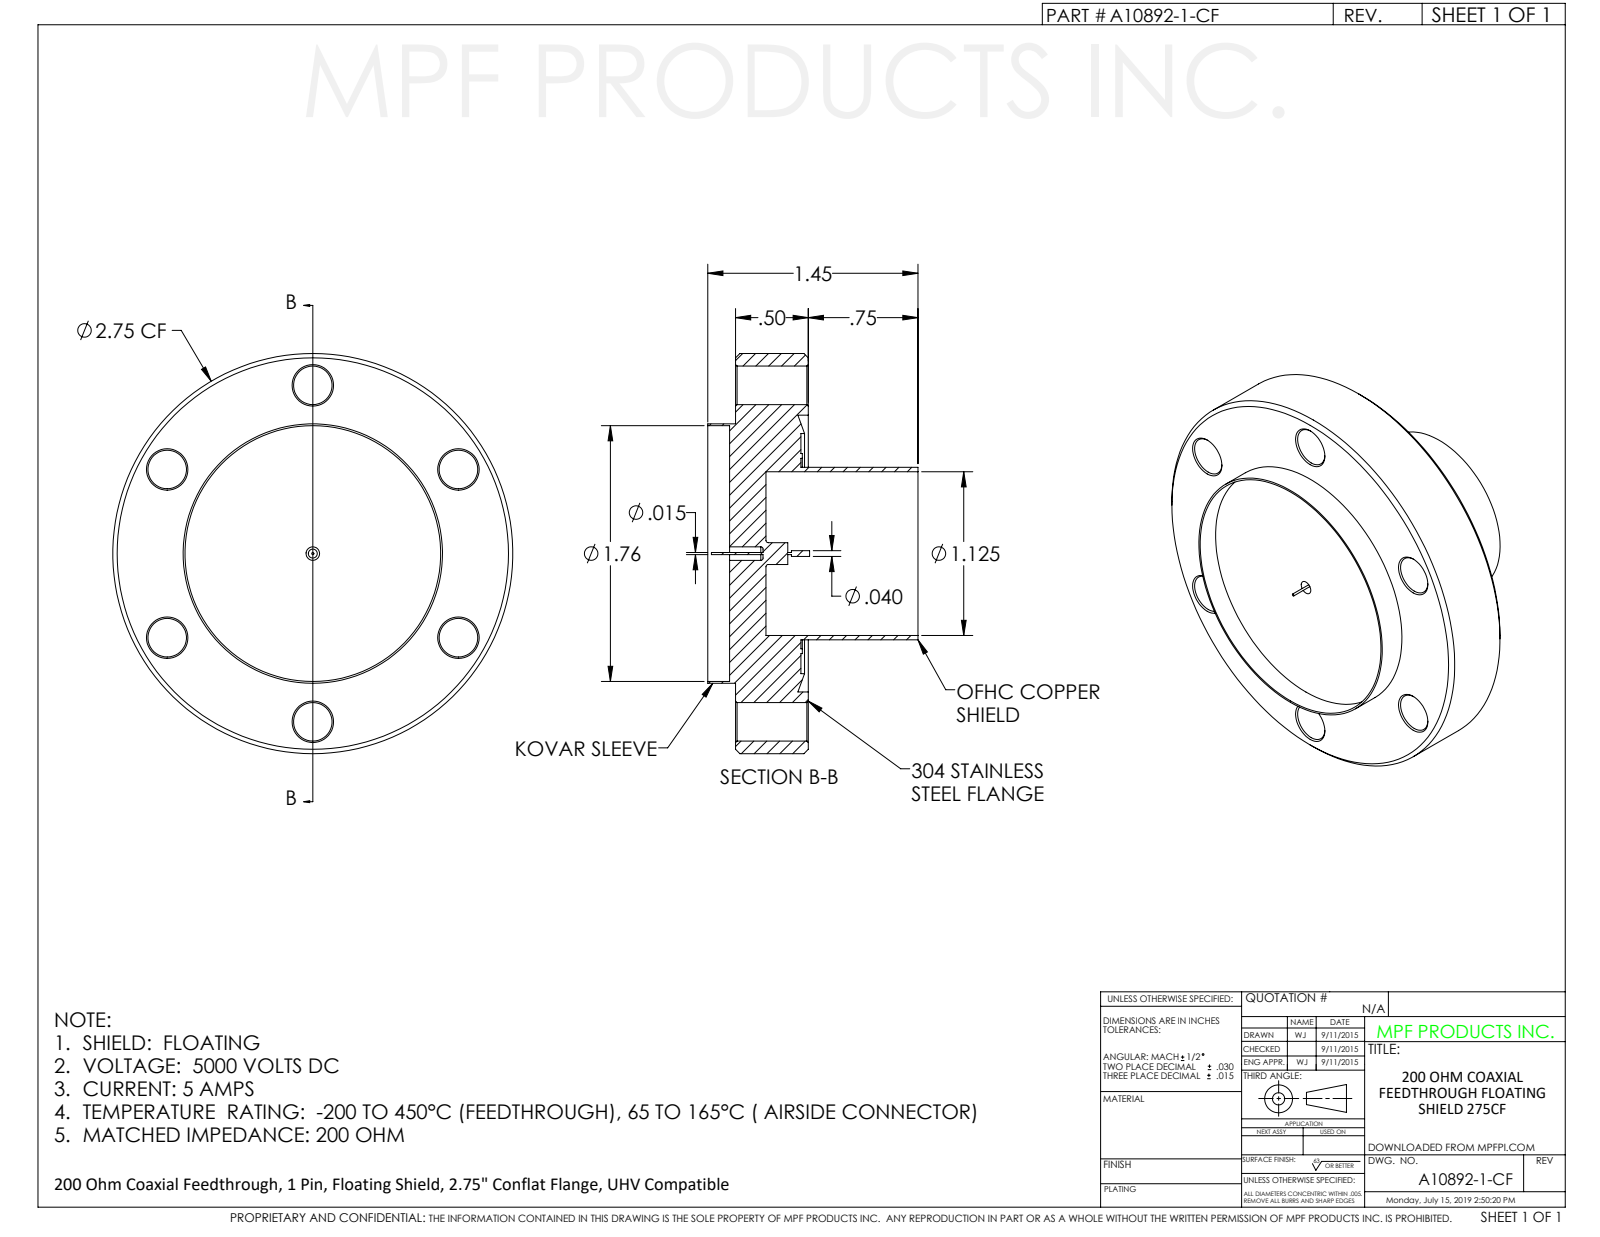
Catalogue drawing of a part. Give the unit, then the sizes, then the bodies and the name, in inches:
Units: inches
Overall size (bounding box): 2.75 × 2.75 × 1.445
Round holes (diameter × count): ⌀0.265 ×6, ⌀0.093 ×1, ⌀1.125 ×1, ⌀1.32 ×1, ⌀1.4 ×1, ⌀1.445 ×1, ⌀1.475 ×1, ⌀1.65 ×1, ⌀1.758 ×1, ⌀1.87 ×1, ⌀1.902 ×1, ⌀1.92 ×1
Round bosses / shafts (diameter × count): ⌀2.75 ×1, ⌀1.945 ×1, ⌀1.895 ×1, ⌀1.783 ×1, ⌀1.546 ×1, ⌀1.5 ×1, ⌀1.49 ×1, ⌀1.425 ×1
Main face-to-face distances: 0.541, 0.041, 0.5, 0.15, 0.225, 0.1, 0.441, 0.059, 0.061, 0.216
Hole centre spacings: 1.156, 2.002, 2.002, 2.312, 2.312
Volume: 2.252 in³ · Surface area: 41.01 in²
Bodies: 1 solid, 135 faces (27 planar, 66 cylindrical, 42 other)
Part name (STEP PRODUCT): A10892-1-CF
STEP written by: SolidWorks 2012 (CONFIG_CONTROL_DESIGN)
